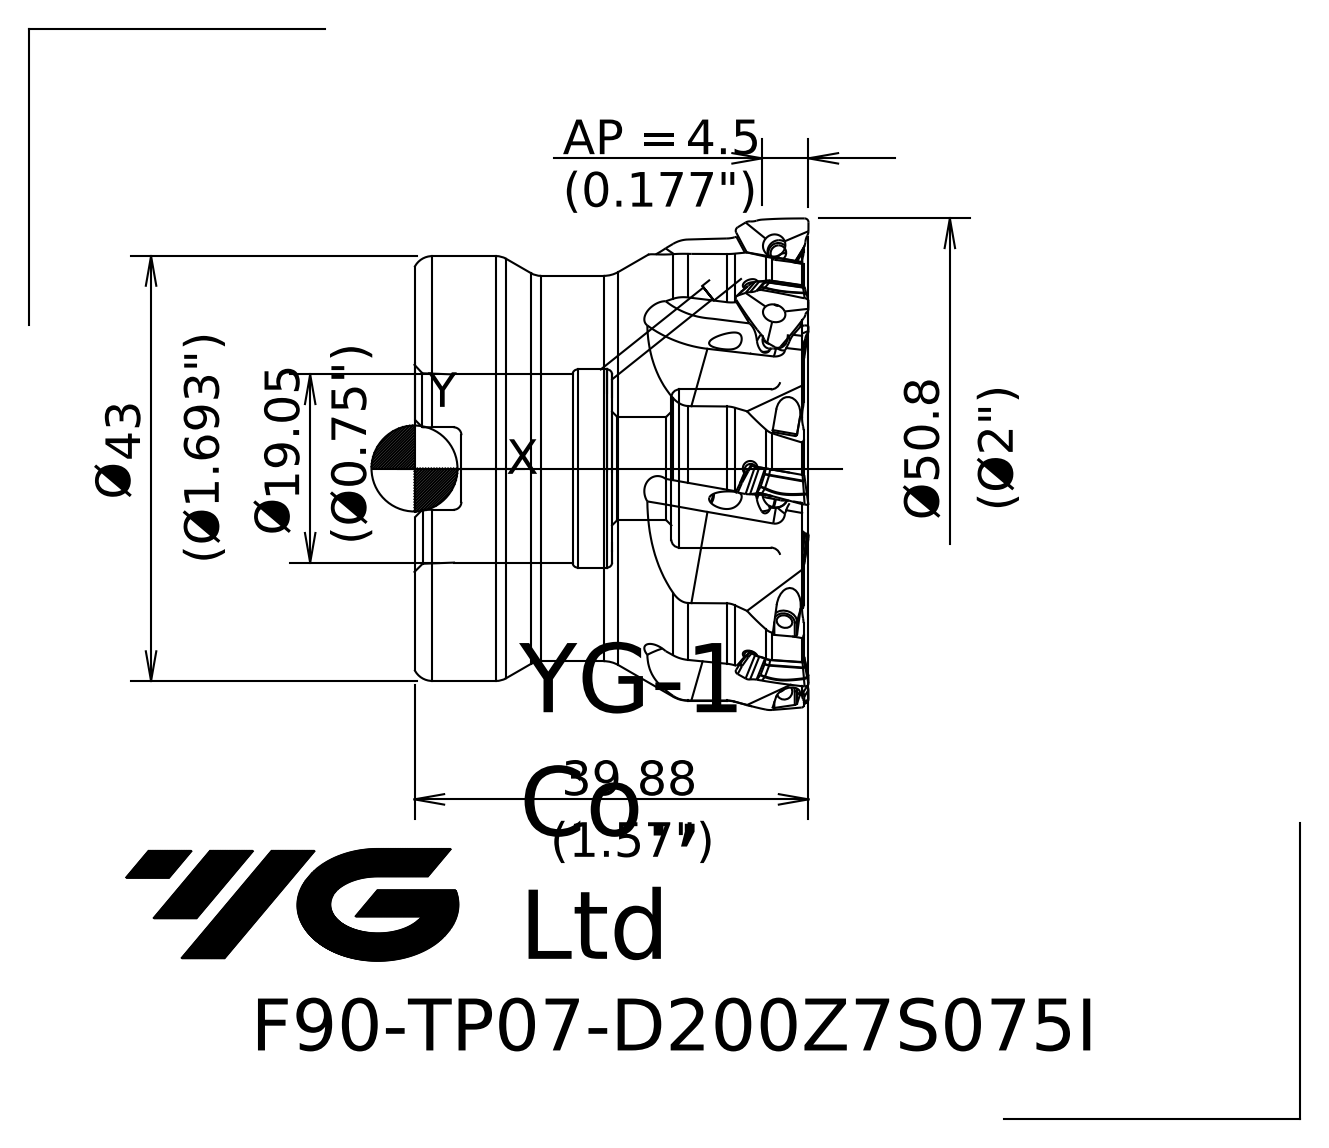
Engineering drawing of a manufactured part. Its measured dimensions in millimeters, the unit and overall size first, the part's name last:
Units: millimetres
Overall size (bounding box): 50.86 × 50.86 × 39.88
Round holes (diameter × count): ⌀10.5 ×1, ⌀16 ×1, ⌀19.05 ×1, ⌀20.05 ×1
Round bosses / shafts (diameter × count): ⌀47 ×1, ⌀43 ×1, ⌀39 ×1
Partial cylindrical surfaces — rounded edges, fillets, slot ends (radius × count): R0.8 ×2
Main face-to-face distances: 0.38, 35.4, 35.02, 3.83, 4.21, 39.23, 19.23, 15.4, 15.02, 20
Volume: 53 292 mm³ · Surface area: 16 212 mm²
Bodies: 2 solids, 75 faces (18 planar, 11 cylindrical, 46 other)
Part name (STEP PRODUCT): 102246548C39fkhm
STEP written by: SIEMENS PLM Software NX 10.0 (AP203_CONFIGURATION_CONTROLLED_3D_DESIGN_OF_MECHANICAL_PARTS_AND_ASSEMBLIES_MIM_LF)
